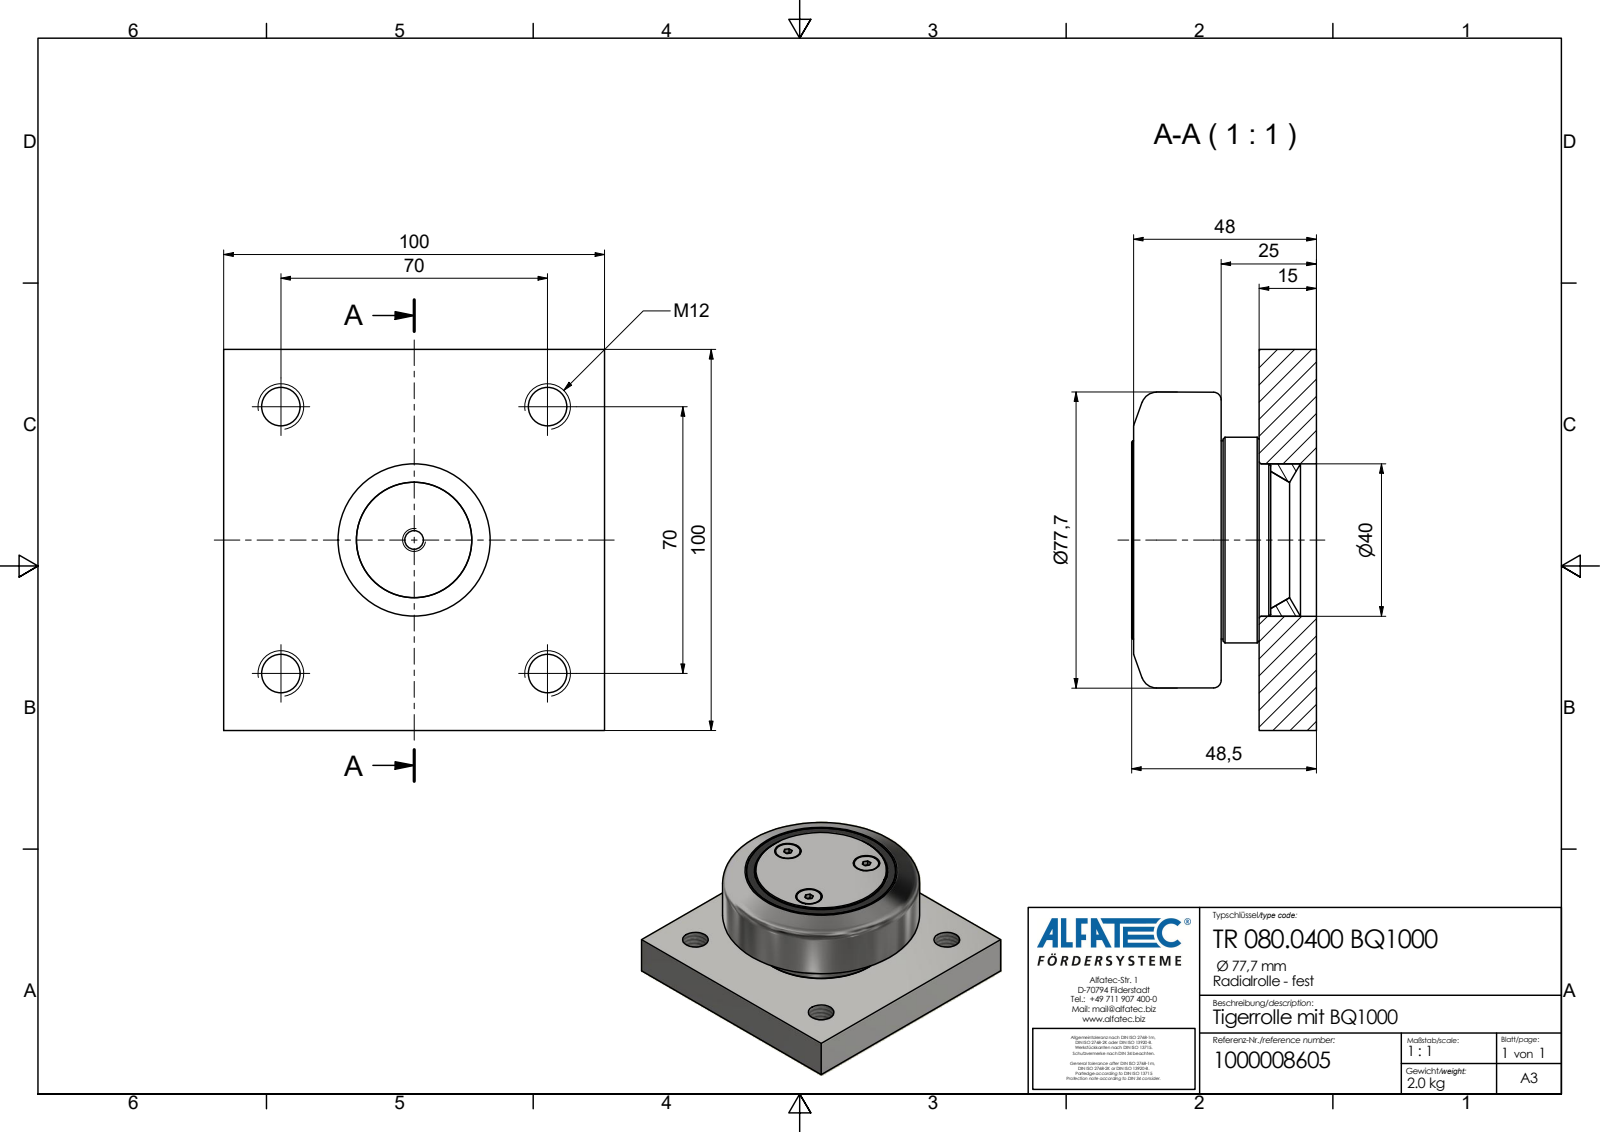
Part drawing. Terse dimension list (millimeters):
name: XTR 080.0400 BQ1000_Kontur
written by: Autodesk Inventor 2020 (AP242_MANAGED_MODEL_BASED_3D_ENGINEERING_MIM_LF)
unit: mm
bodies: 1 solid, 62 faces (39 planar, 15 cylindrical, 8 other)
size: 100 × 100 × 48.5
volume: 275 516 mm³; area: 40 913 mm²
holes: 4× ⌀10.11, 3× ⌀10.4, 1× ⌀4.92, 1× ⌀40
bosses: 3× ⌀9.75, 1× ⌀54, 1× ⌀52
face distances: 15, 100, 25, 10, 23.5, 48.5, 33.5, 0.5, 48, 33
hole spacings: 49.5, 70, 18.5, 32.04, 31.99, 38.69, 48.15, 57.15
